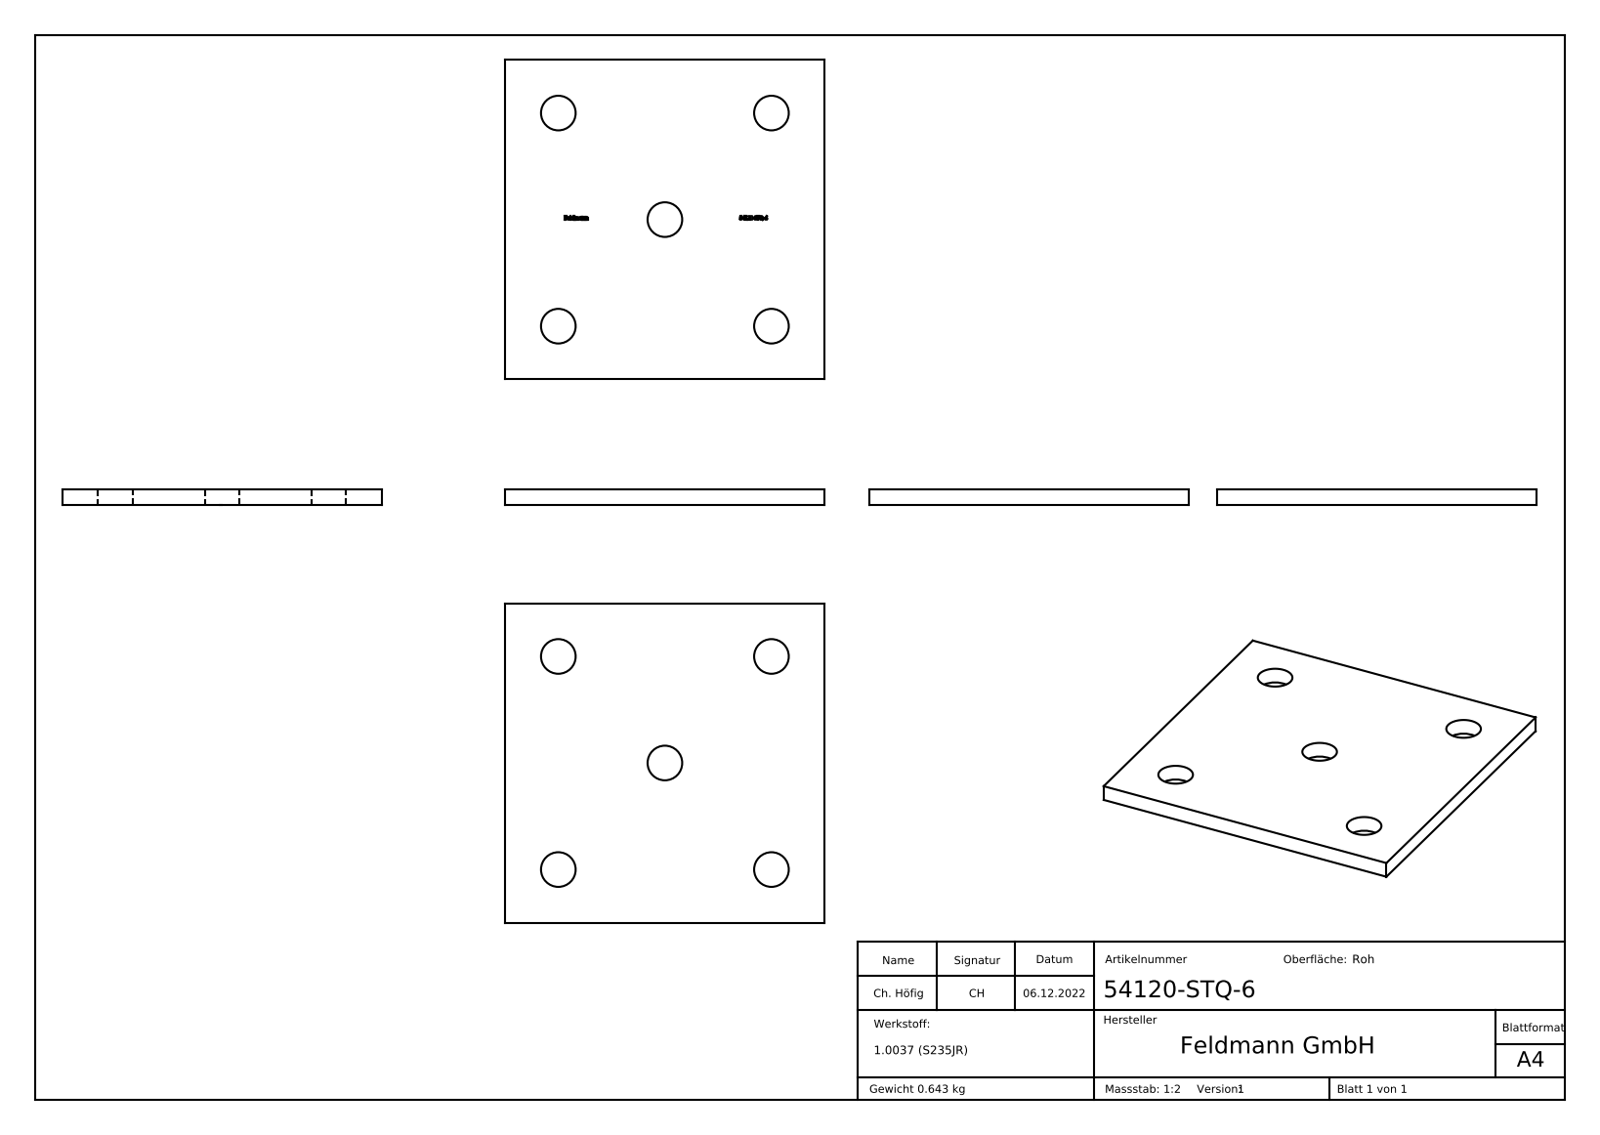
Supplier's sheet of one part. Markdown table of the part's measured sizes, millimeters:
| quantity | value |
| --- | --- |
| part name | 54120-STQ-6 |
| STEP written by | SolidWorks 2018 (CONFIG_CONTROL_DESIGN) |
| units | millimeters |
| bodies | 1 solid, 254 faces (144 planar, 5 cylindrical, 105 other) |
| overall size | 120 × 120 × 6 |
| volume | 82 417 mm³ |
| surface area | 31 588 mm² |
| round holes (diameter × count) | 13 × 5 |
| main face-to-face distances | 6, 120, 5.9, 60, 1.32, 0.44, 0.88, 4.43, 67.98, 72.41 |
| hole center spacings | 56.57, 80, 113.14 |
